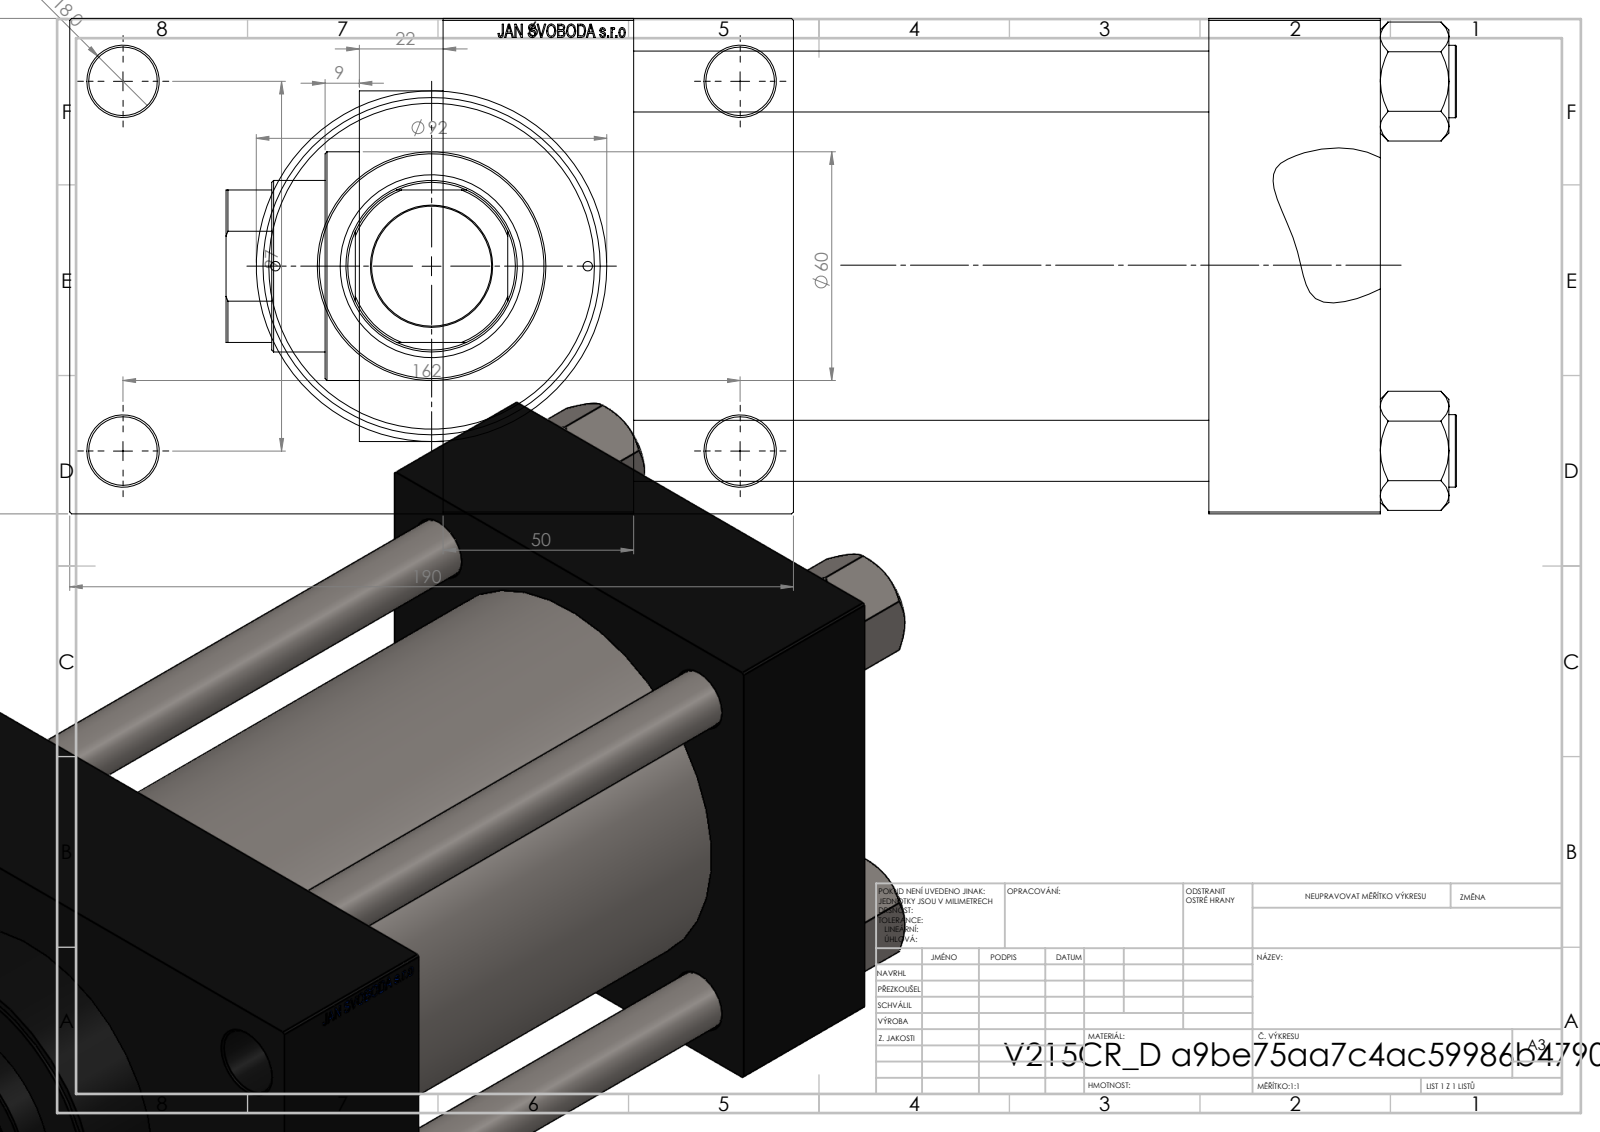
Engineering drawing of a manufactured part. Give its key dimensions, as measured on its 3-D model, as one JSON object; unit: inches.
{"part_name": "NUT_M5_D; V215_VC_A; V215CR_D_Body; V215CR_D_TYCINKA (+1 more)", "step_written_by": "SolidWorks 2019 (CONFIG_CONTROL_DESIGN)", "units": "inches", "bodies": {"solids": 11, "faces": 1159, "planar": 547, "cylindrical": 92, "other": 520}, "overall_size": [12.717, 7.48, 5.118], "volume_in3": 174.5, "surface_area_in2": 672.5, "round_holes": [[0.63, 4], [0.709, 4], [0.098, 2], [0.276, 2], [1.041, 2], [1.378, 2], [1.24, 1], [1.772, 1], [1.89, 1], [2.992, 1], [3.366, 1], [3.937, 1]], "round_bosses_or_shafts": [[0.748, 4], [4.173, 1], [3.622, 1], [2.362, 1]], "partial_cylinders_radius": [[0.866, 1]], "face_to_face_distances": [5.118, 1.772, 7.717, 5.945, 9.685, 7.913, 1.969, 1.181, 6.299, 3.78], "hole_center_spacings": [1.281, 1.93, 2.475, 2.698, 3.717, 3.815, 4.005, 4.026]}
